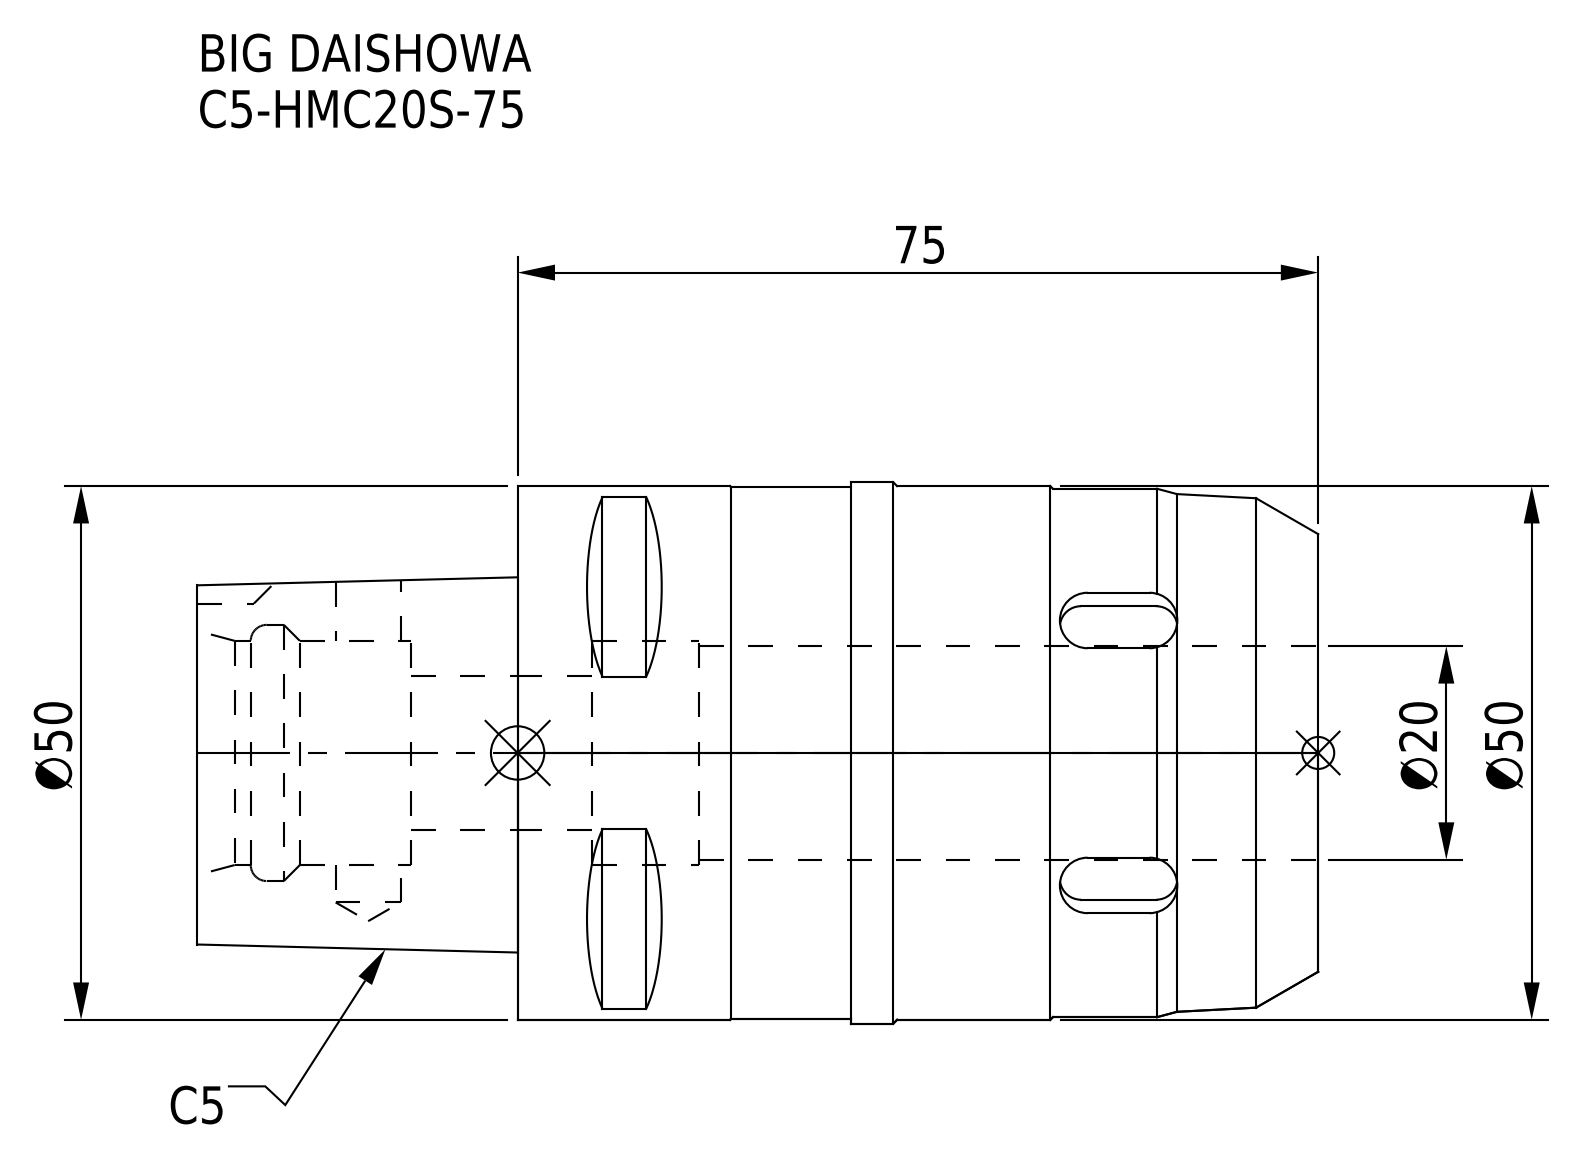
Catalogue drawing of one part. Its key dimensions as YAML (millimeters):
part_name: "C5-HMC20S-75"
step_written_by: "CREO PARAMETRIC BY PTC INC, 2016380 (AUTOMOTIVE_DESIGN)"
units: millimeters
bodies: {solids: 1, faces: 112, planar: 47, cylindrical: 39, other: 26}
overall_size: [105, 50.7, 50.7]
volume: 136896
surface_area: 25221
round_holes:
  - {diameter: 6.1, count: 1}
  - {diameter: 14.5, count: 1}
  - {diameter: 20, count: 1}
  - {diameter: 21, count: 1}
  - {diameter: 24, count: 1}
round_bosses_or_shafts:
  - {diameter: 50.7, count: 1}
  - {diameter: 50, count: 1}
  - {diameter: 49.8, count: 1}
  - {diameter: 49.5, count: 1}
partial_cylinders:
  - {radius: 3, count: 6}
  - {radius: 4, count: 1}
face_to_face_distances: [75, 105, 30, 10, 17, 44, 68, 85, 7, 37]
